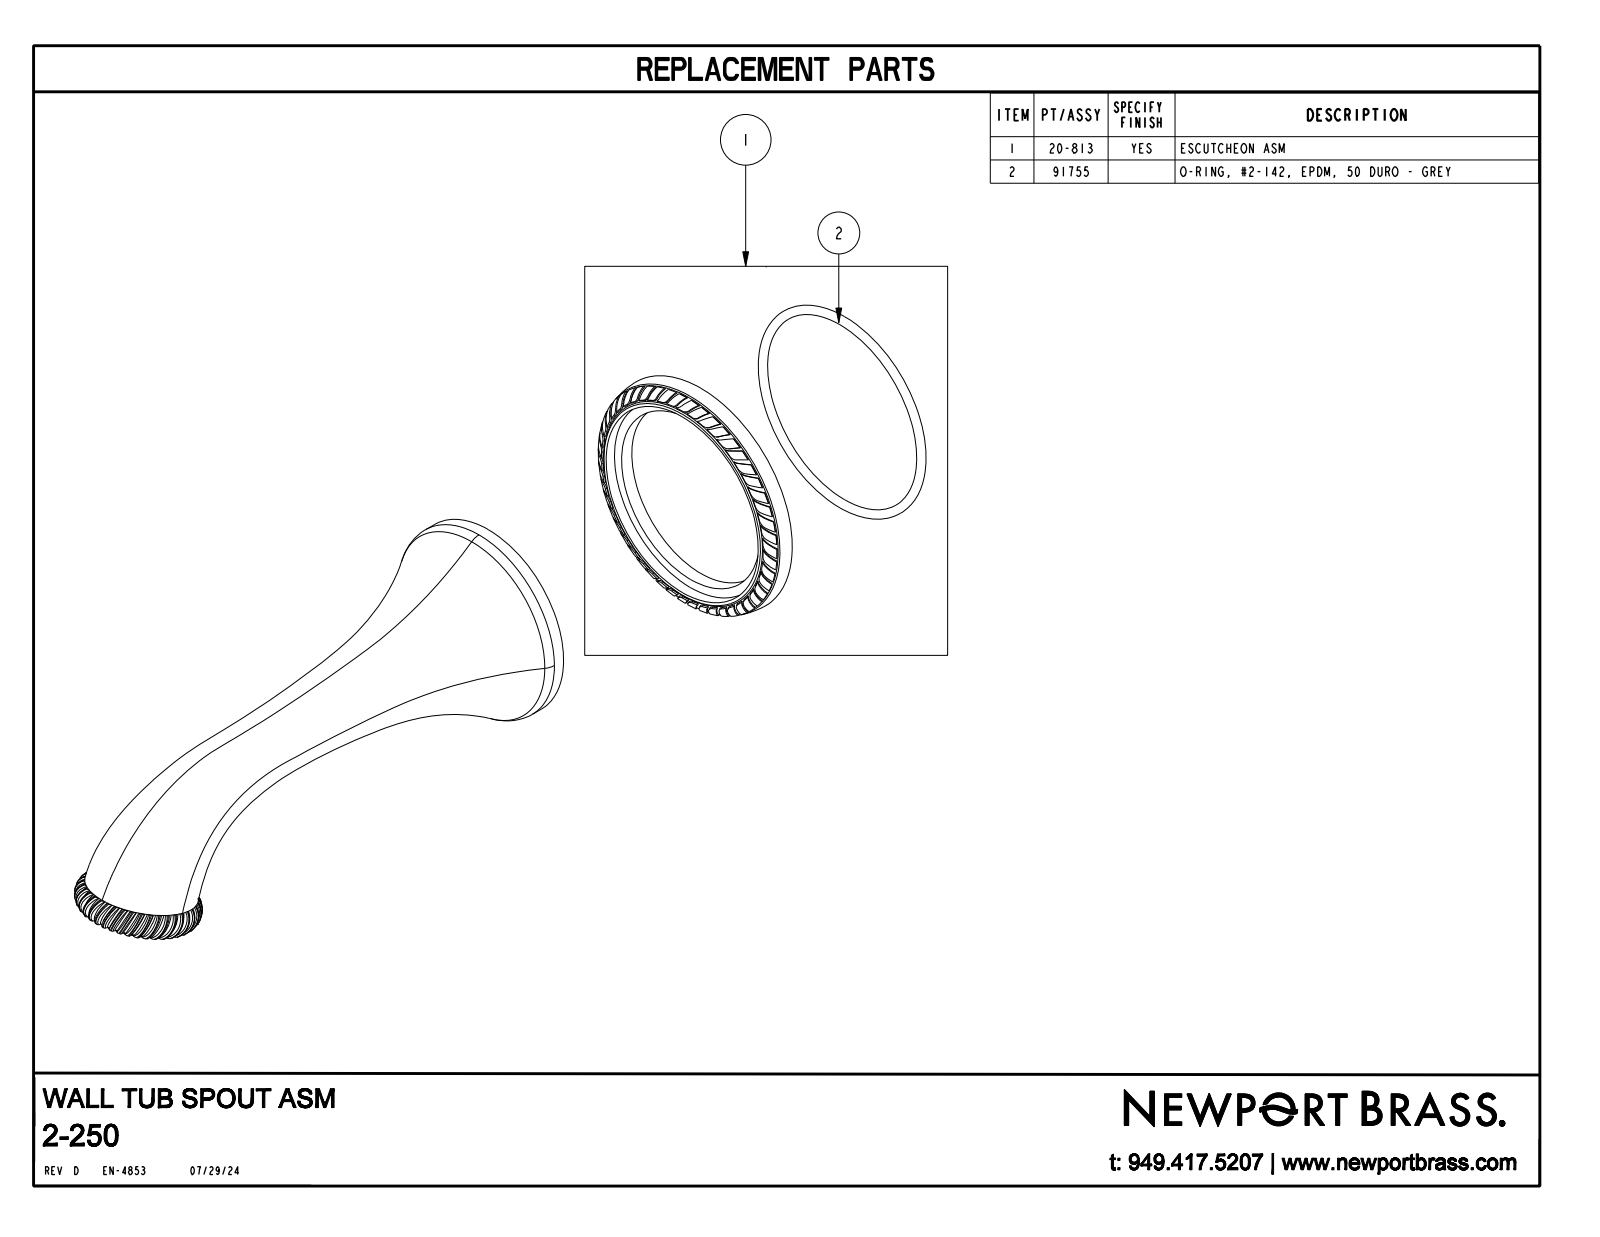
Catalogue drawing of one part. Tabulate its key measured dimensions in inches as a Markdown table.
| quantity | value |
| --- | --- |
| part name | 10086; 10438; 10852; 91755 (+1 more) |
| STEP written by | CREO PARAMETRIC BY PTC INC, 2018400 (AUTOMOTIVE_DESIGN) |
| units | inches |
| bodies | 4 solids, 786 faces (108 planar, 186 cylindrical, 492 other) |
| overall size | 6.295 × 2.845 × 2.845 |
| volume | 9.728 in³ |
| surface area | 51.25 in² |
| round bosses / shafts (diameter × count) | 2.345 × 1, 1.705 × 1, 1.102 × 1 |
| partial cylindrical surfaces (radius × count) | 0.15 × 49, 0.224 × 40, 0.09 × 25, 0.12 × 24, 0.121 × 1, 0.137 × 1 |
| main face-to-face distances | 0.29, 0.28, 0.16, 0.15, 0.13, 0.295, 0.296, 0.291, 0.097, 0.105 |
